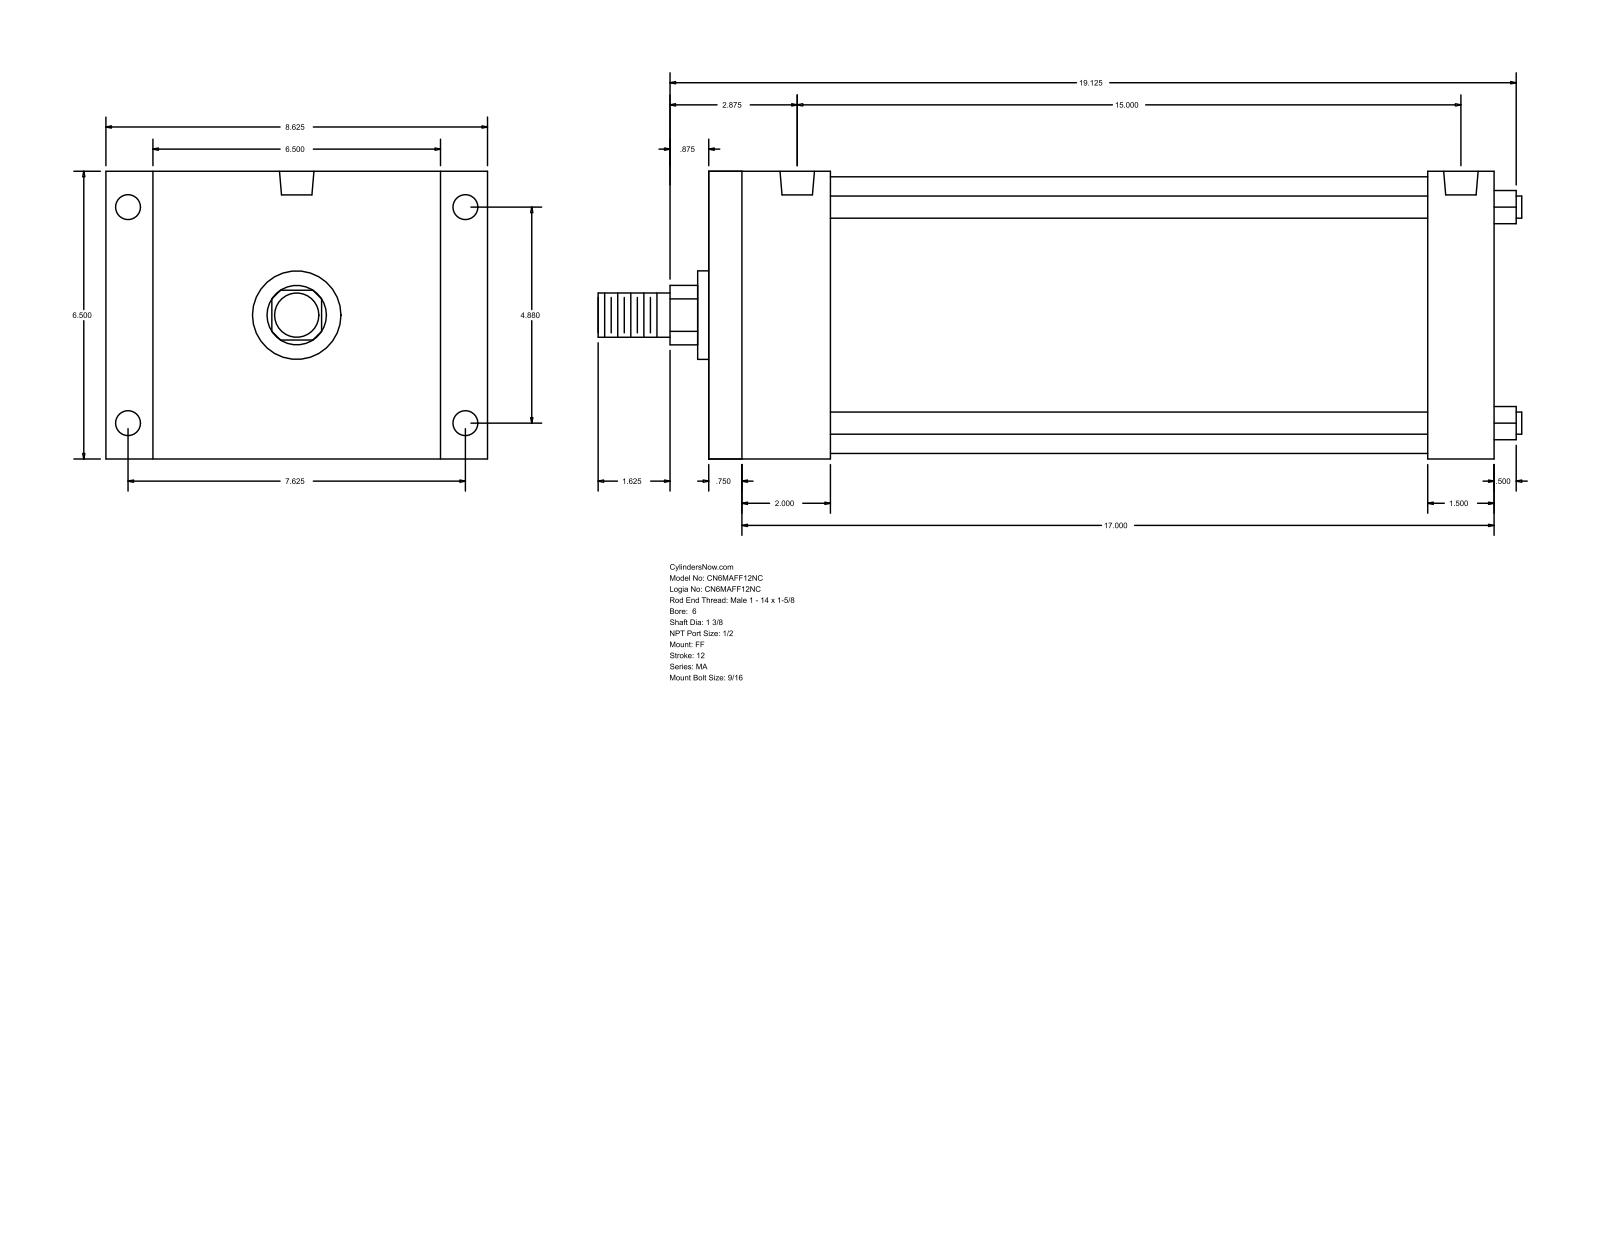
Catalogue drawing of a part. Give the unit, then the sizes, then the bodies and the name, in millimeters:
Units: millimetres
Overall size (bounding box): 530.23 × 219.07 × 165.1
Round holes (diameter × count): ⌀14.29 ×4, ⌀17.46 ×4, ⌀19.77 ×2
Round bosses / shafts (diameter × count): ⌀12.7 ×4, ⌀158.75 ×1, ⌀50.8 ×1, ⌀34.92 ×1, ⌀25.4 ×1
Partial cylindrical surfaces — rounded edges, fillets, slot ends (radius × count): R17.06 ×1
Main face-to-face distances: 165.1, 450.84, 15.87, 434.97, 66.67, 50.8, 384.17, 412.75, 396.88, 346.08
Hole centre spacings: 123.96, 193.68, 229.95, 384.17, 3.18, 380.99
Bodies: 0 solids, 92 faces (64 planar, 28 cylindrical, 0 other)
Part name (STEP PRODUCT): MA_FF__0600_1.375
STEP written by: GSSL Pune (CONFIG_CONTROL_DESIGN)
